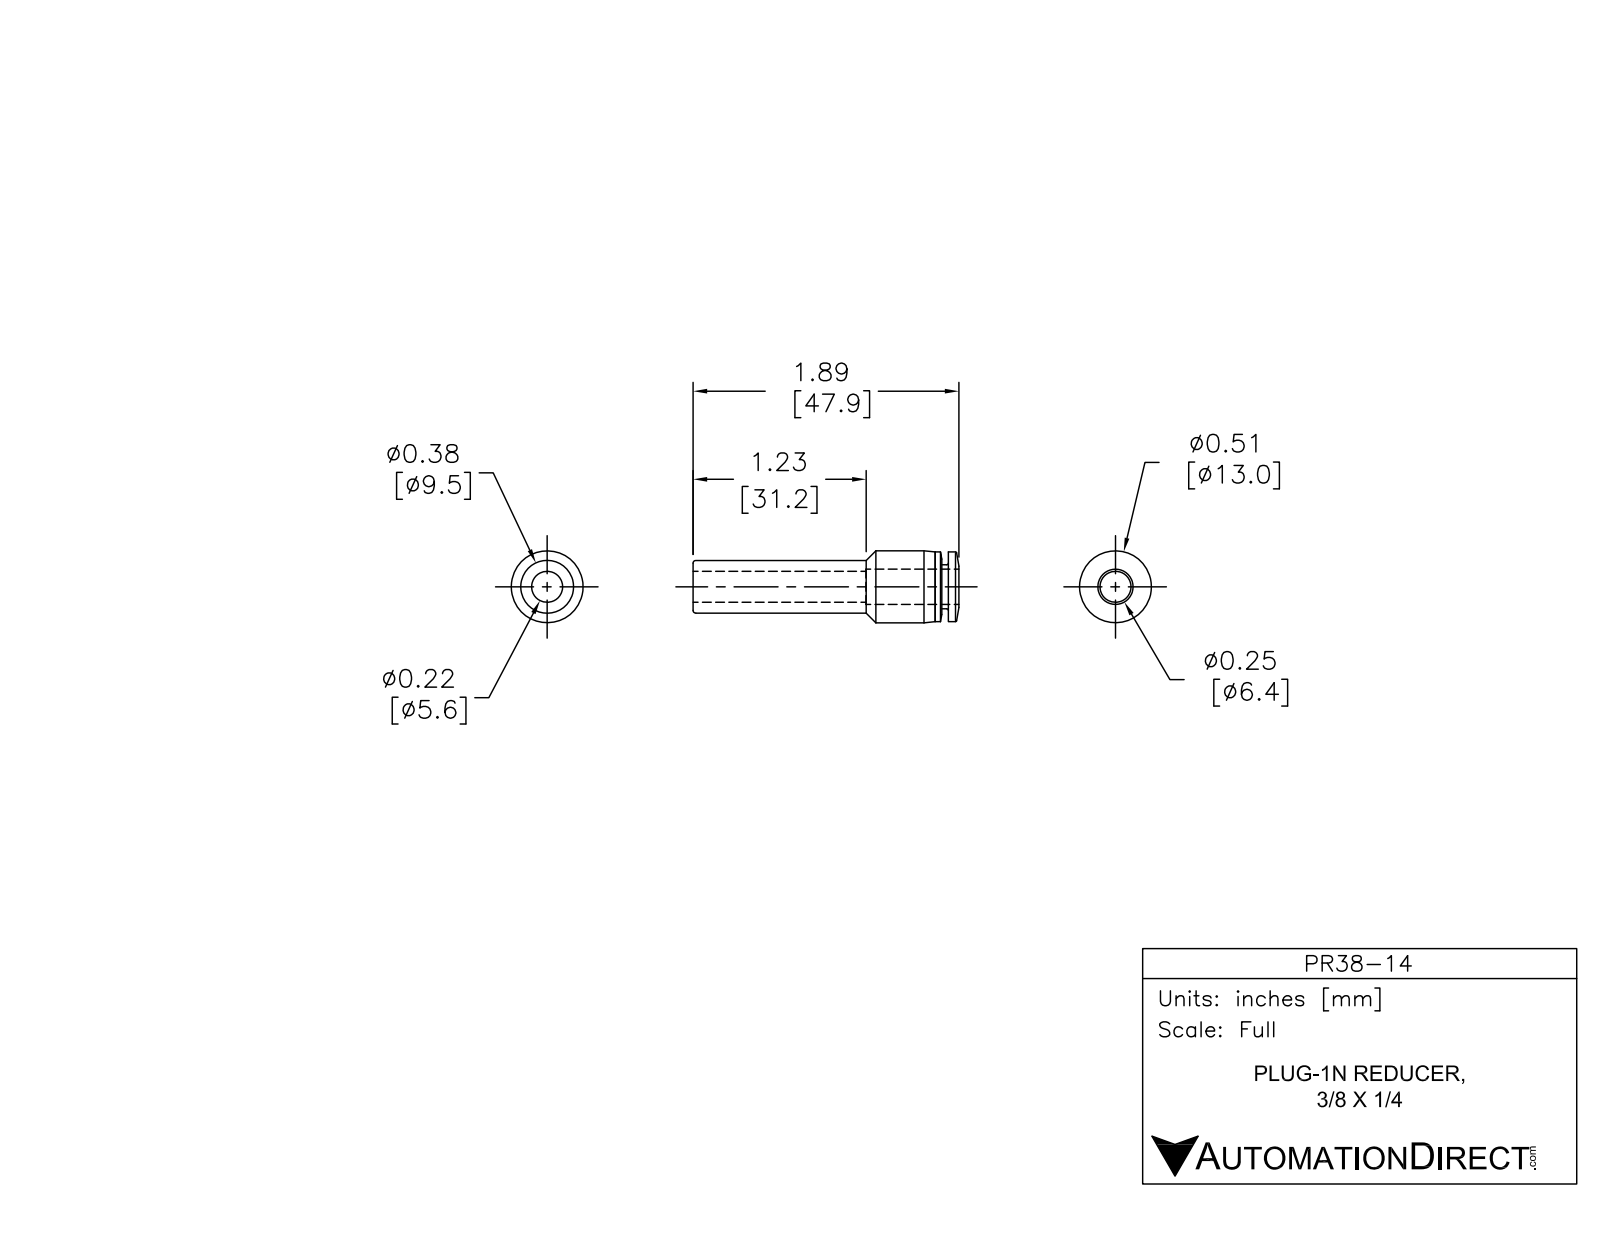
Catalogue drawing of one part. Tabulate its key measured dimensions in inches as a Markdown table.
| quantity | value |
| --- | --- |
| part name | PR38-14 |
| STEP written by | SolidWorks 2015 (AUTOMOTIVE_DESIGN) |
| units | inches |
| bodies | 1 solid, 36 faces (4 planar, 14 cylindrical, 18 other) |
| overall size | 1.89 × 0.512 × 0.512 |
| volume | 0.176 in³ |
| surface area | 4.275 in² |
| round holes (diameter × count) | 0.22 × 1, 0.258 × 1 |
| round bosses / shafts (diameter × count) | 0.512 × 1, 0.496 × 1, 0.374 × 1, 0.313 × 1 |
| main face-to-face distances | 1.815, 1.768, 0.047, 1.228, 0.539, 0.587 |
